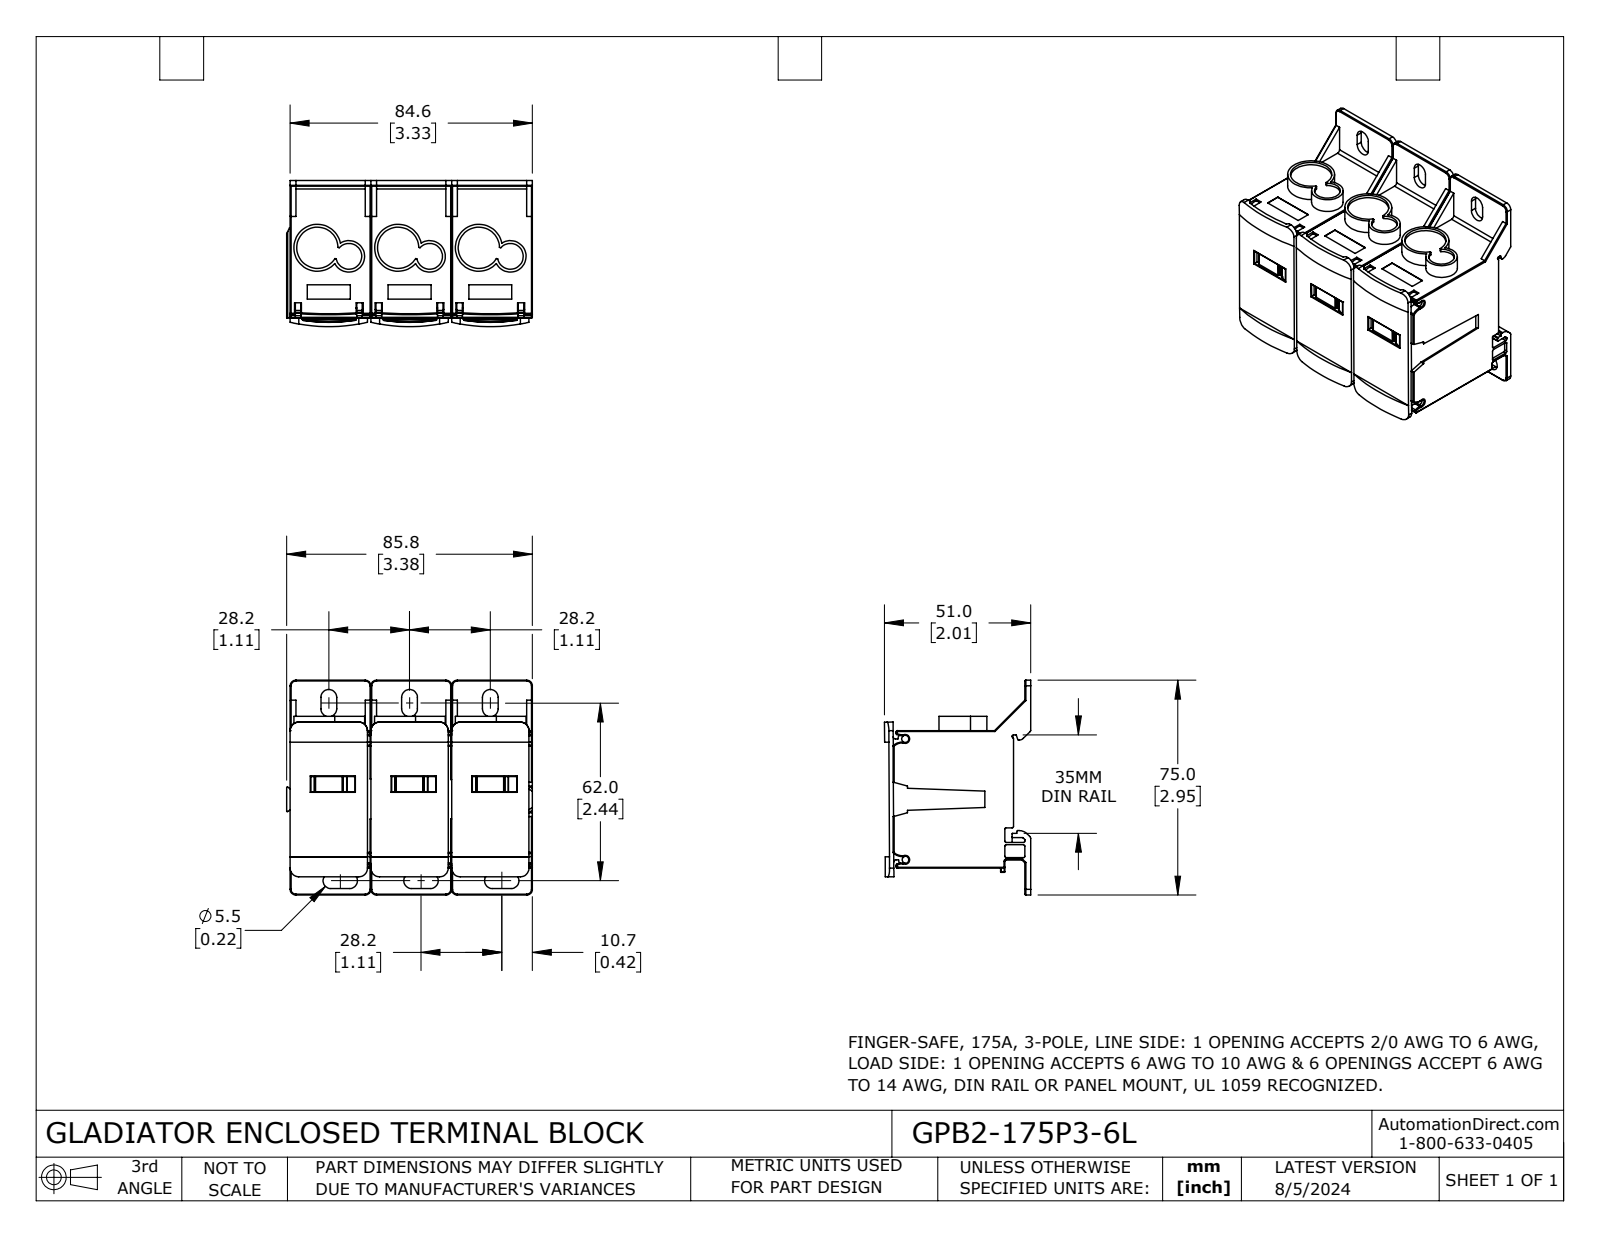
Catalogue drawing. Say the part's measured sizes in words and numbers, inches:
The part is named "GPB2-175P3-6L". Its 3-D file was written by "SolidWorks 2023 (CONFIG_CONTROL_DESIGN)". It is 1 solid with 1243 faces: 417 planar, 616 cylindrical and 210 other. Overall it measures 3.378 by 2.953 by 2.009 inches. Its volume is 11.29 cubic inches and its surface area 54.43 square inches. Round holes: 3 of diameter 0.354, 3 of diameter 0.567, 1 of diameter 0.098. Round bosses or shafts: 3 of diameter 0.646, 1 of diameter 0.098. Partial cylindrical surfaces (rounded edges, fillets, slot ends): 149 of radius 0.008, 77 of radius 0.012, 24 of radius 0.02, 13 of radius 0.079, 13 of radius 0.197, 12 of radius 0.108, 12 of radius 0.118, 9 of radius 0.207. The main face-to-face distances are 0.157, 0.079, 0.236, 0.039, 3.331, 1.89, 1.85, 0.059, 0.276, 2.047. The hole center spacings are 1.11, 0.449, 0.687, 1.548, 2.22, 1.791, 2.656.
